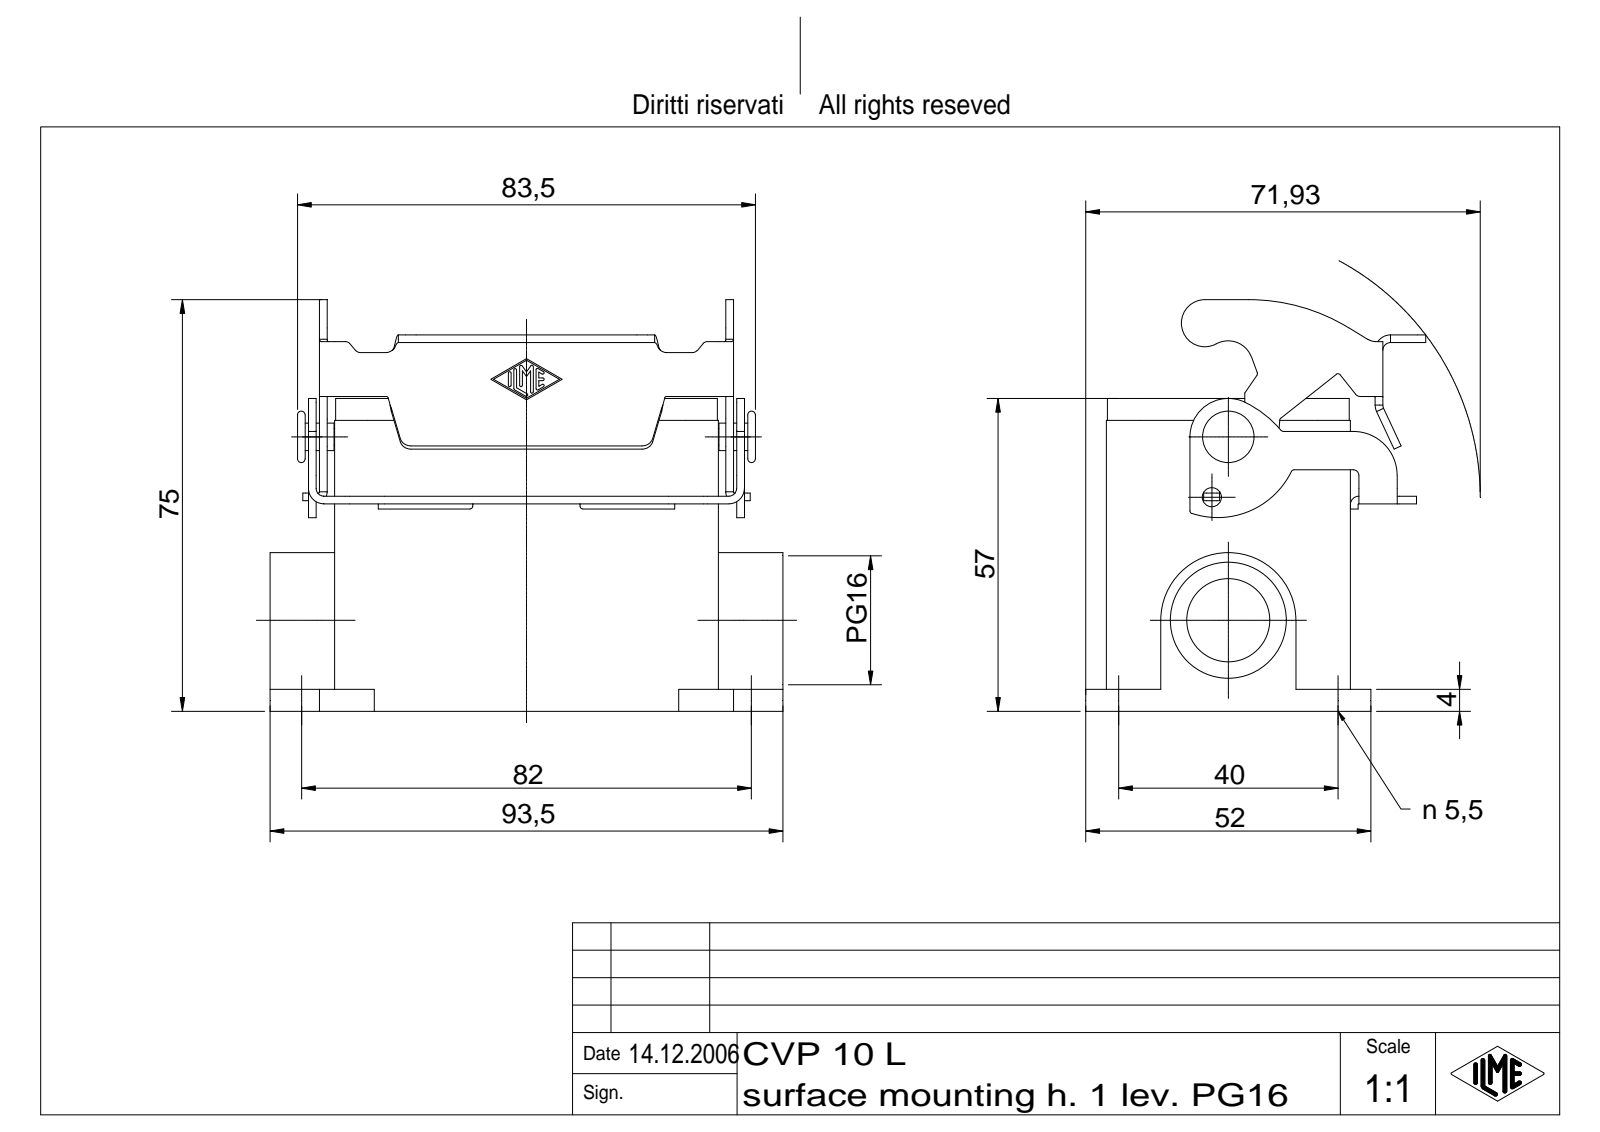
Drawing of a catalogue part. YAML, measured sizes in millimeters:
part_name: "CVP 10 L"
step_written_by: "Autodesk Inventor 7 (AUTOMOTIVE_DESIGN)"
units: millimeters
bodies: {solids: 2, faces: 401, planar: 141, cylindrical: 116, other: 144}
overall_size: [93.5, 75, 61.98]
volume: 81774
surface_area: 45387
round_holes:
  - {diameter: 5.5, count: 4}
  - {diameter: 3.5, count: 1}
  - {diameter: 15.16, count: 1}
  - {diameter: 21.16, count: 1}
round_bosses_or_shafts:
  - {diameter: 5, count: 1}
  - {diameter: 3.2, count: 1}
  - {diameter: 3, count: 1}
partial_cylinders:
  - {radius: 0.25, count: 15}
  - {radius: 0.5, count: 9}
  - {radius: 1.5, count: 9}
  - {radius: 1, count: 8}
  - {radius: 1.4, count: 6}
  - {radius: 2, count: 6}
  - {radius: 2.8, count: 6}
  - {radius: 1.8, count: 4}
face_to_face_distances: [4, 40.5, 44.5, 36.5, 1.4, 10, 60, 6, 40.3, 66]
hole_center_spacings: [40, 82, 91.24, 22.62]
